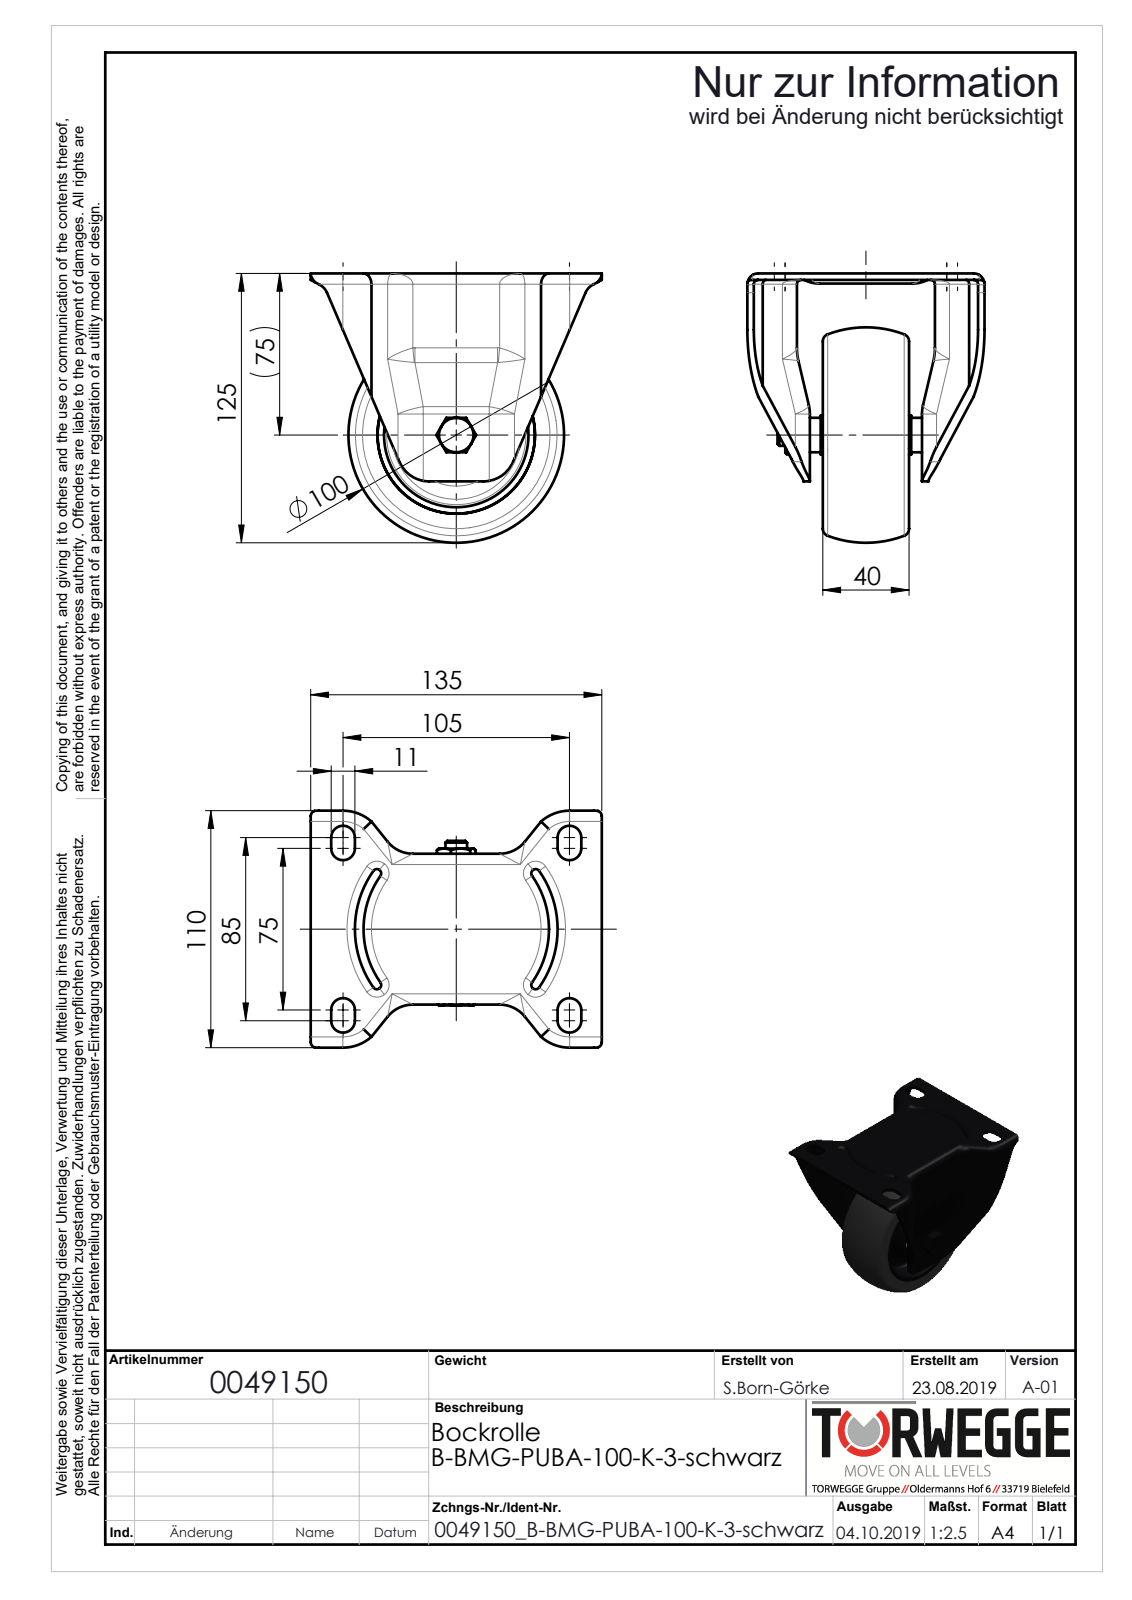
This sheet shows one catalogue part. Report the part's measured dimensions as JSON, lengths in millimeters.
{"part_name": "0049150_B-BMG-PUBA-100-K-3-schwarz_(A-01)", "step_written_by": "SolidWorks 2018 (AUTOMOTIVE_DESIGN)", "units": "millimeters", "bodies": {"solids": 14, "faces": 452, "planar": 126, "cylindrical": 152, "other": 174}, "overall_size": [135, 125, 110], "volume_mm3": 314845, "surface_area_mm2": 135721, "round_holes": [[8.5, 1], [10, 1], [10.1, 1], [10.2, 1], [12, 1], [12.4, 1], [18, 1], [26, 1]], "round_bosses_or_shafts": [[32, 1], [16, 1], [15, 1], [11.9, 1]], "partial_cylinders_radius": [[15, 16], [18, 14], [2, 8], [5, 8], [5.5, 8], [2.5, 4], [17, 4], [20, 4]], "face_to_face_distances": [3, 6, 55, 9, 61, 30, 16, 52, 1.8, 64]}
